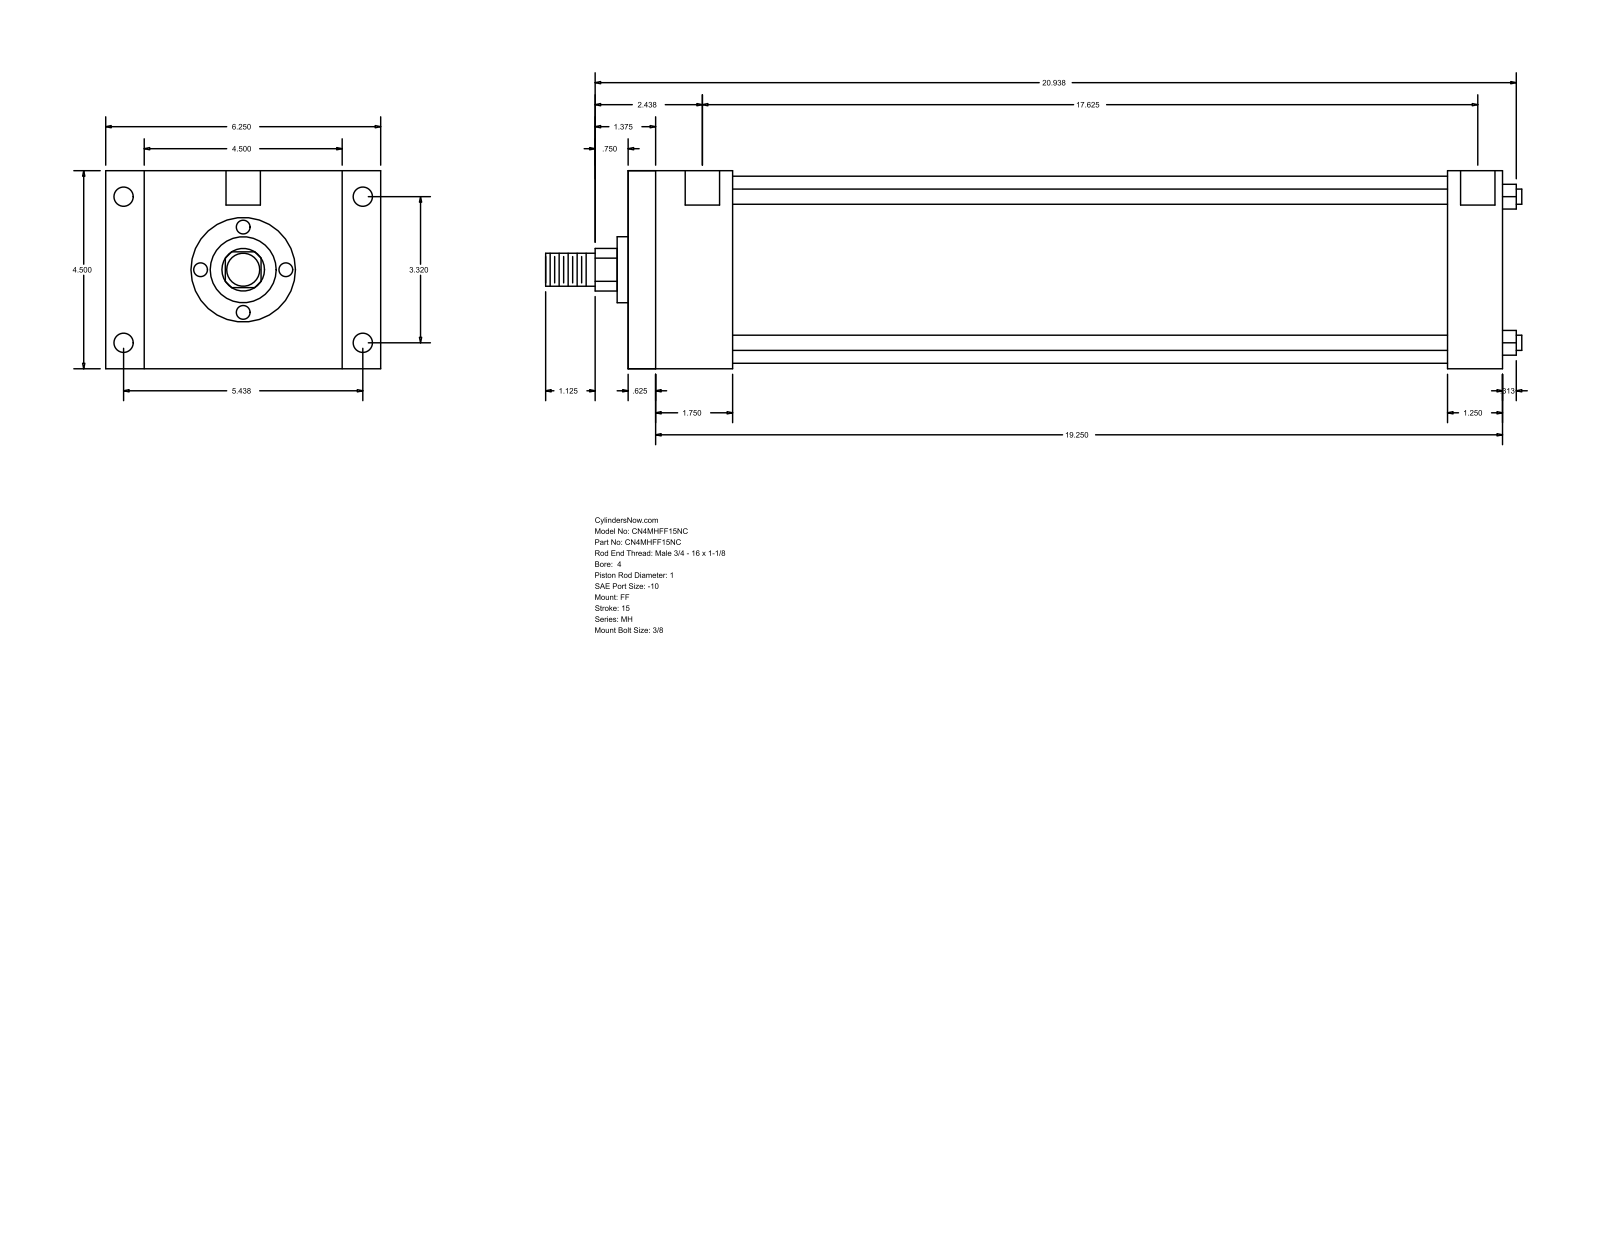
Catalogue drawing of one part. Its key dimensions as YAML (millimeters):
part_name: "MH_FF__0400_1"
step_written_by: "GSSL Pune (CONFIG_CONTROL_DESIGN)"
units: millimeters
bodies: {solids: 0, faces: 92, planar: 64, cylindrical: 28, other: 0}
overall_size: [563.56, 158.75, 114.3]
round_holes:
  - {diameter: 8.73, count: 4}
  - {diameter: 11.13, count: 4}
  - {diameter: 19.84, count: 2}
round_bosses_or_shafts:
  - {diameter: 8.76, count: 4}
  - {diameter: 107.95, count: 1}
  - {diameter: 38.1, count: 1}
  - {diameter: 25.4, count: 1}
  - {diameter: 19.05, count: 1}
partial_cylinders:
  - {radius: 12.29, count: 1}
face_to_face_distances: [114.3, 504.83, 15.87, 488.96, 60.33, 44.46, 444.5, 473.07, 457.2, 412.74]
hole_center_spacings: [84.32, 138.12, 161.82, 450.85, 1.58, 1.59, 447.68, 449.26]
